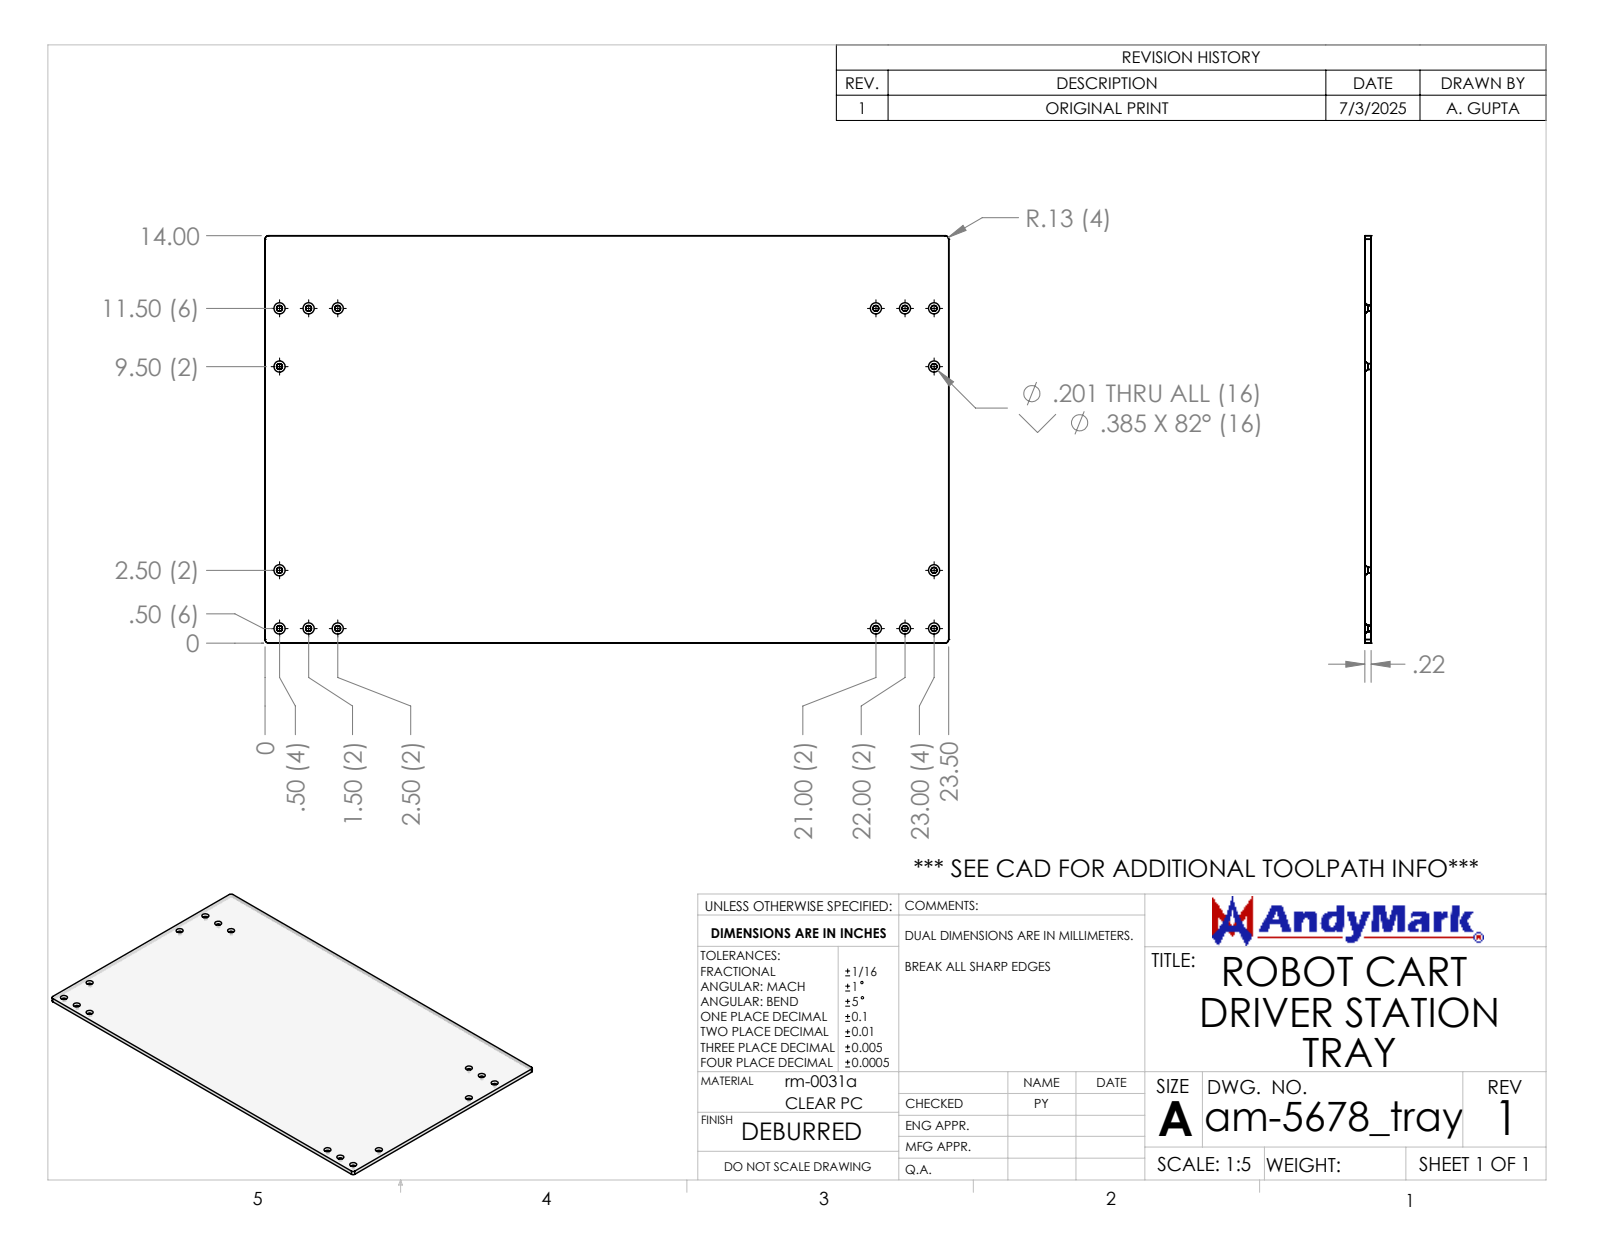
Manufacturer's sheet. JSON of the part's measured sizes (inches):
{"part_name": "am-5678_tray Robot Cart Driver Station Tray", "step_written_by": "SolidWorks 2024 (CONFIG_CONTROL_DESIGN)", "units": "inches", "bodies": {"solids": 1, "faces": 74, "planar": 6, "cylindrical": 36, "other": 32}, "overall_size": [23.5, 14, 0.22], "volume_in3": 72.2, "surface_area_in2": 675.3, "round_holes": [[0.201, 16]], "partial_cylinders_radius": [[0.125, 4]], "face_to_face_distances": [0.22, 14, 23.5], "hole_center_spacings": [1, 2, 11.045, 22.389, 11, 20.5, 23.265, 2.236]}
